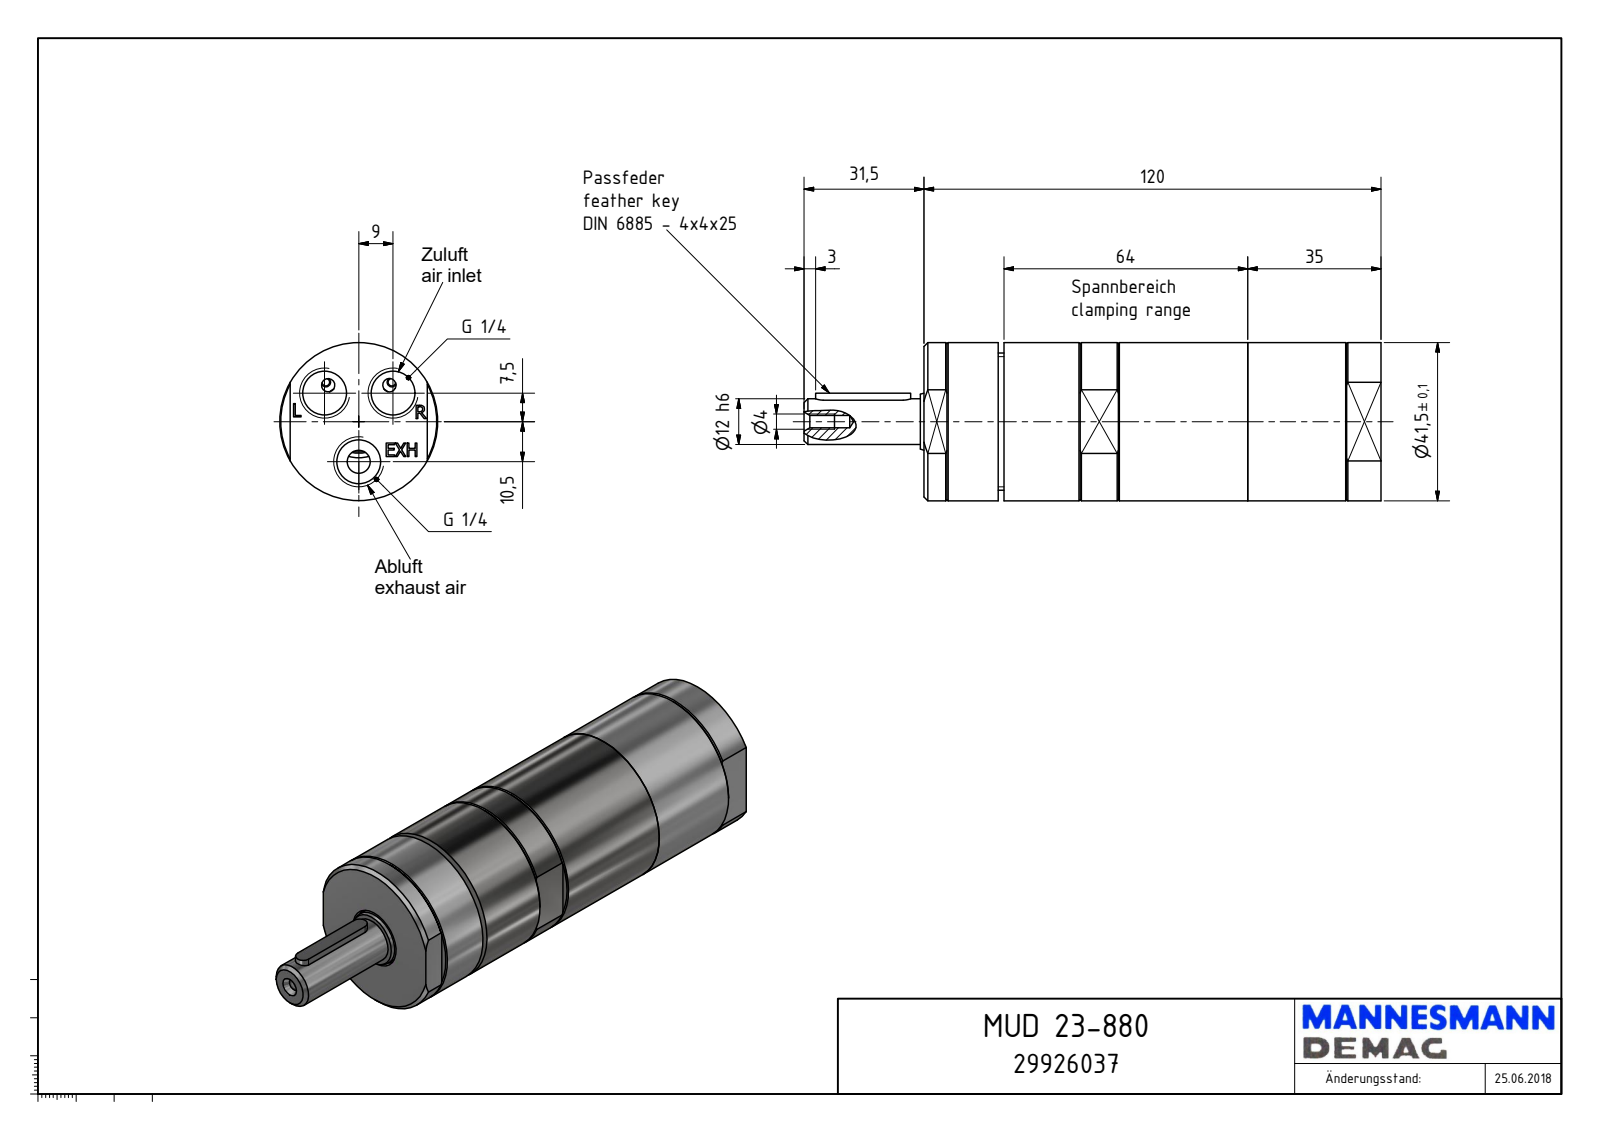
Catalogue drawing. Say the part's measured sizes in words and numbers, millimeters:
The part is named "MUD 23-880_29926037". Its 3-D file was written by "Autodesk Inventor 2018 (AUTOMOTIVE_DESIGN)". It is 1 solid with 138 faces: 86 planar, 21 cylindrical and 31 other. Overall it measures 151.5 by 41.5 by 41.5 millimeters. Its volume is 159 115 cubic millimeters and its surface area 21 901 square millimeters. Round holes: 3 of diameter 11.45, 1 of diameter 3.24, 1 of diameter 6, 1 of diameter 16. Round bosses or shafts: 1 of diameter 41.5, 1 of diameter 39.27, 1 of diameter 14.95, 1 of diameter 12. Partial cylindrical surfaces (rounded edges, fillets, slot ends): 2 of radius 2. The main face-to-face distances are 120, 1, 37, 38, 102.98, 17.02, 21, 36, 81.98, 99. The hole center spacings are 11.72, 20.12, 10.5, 18.
